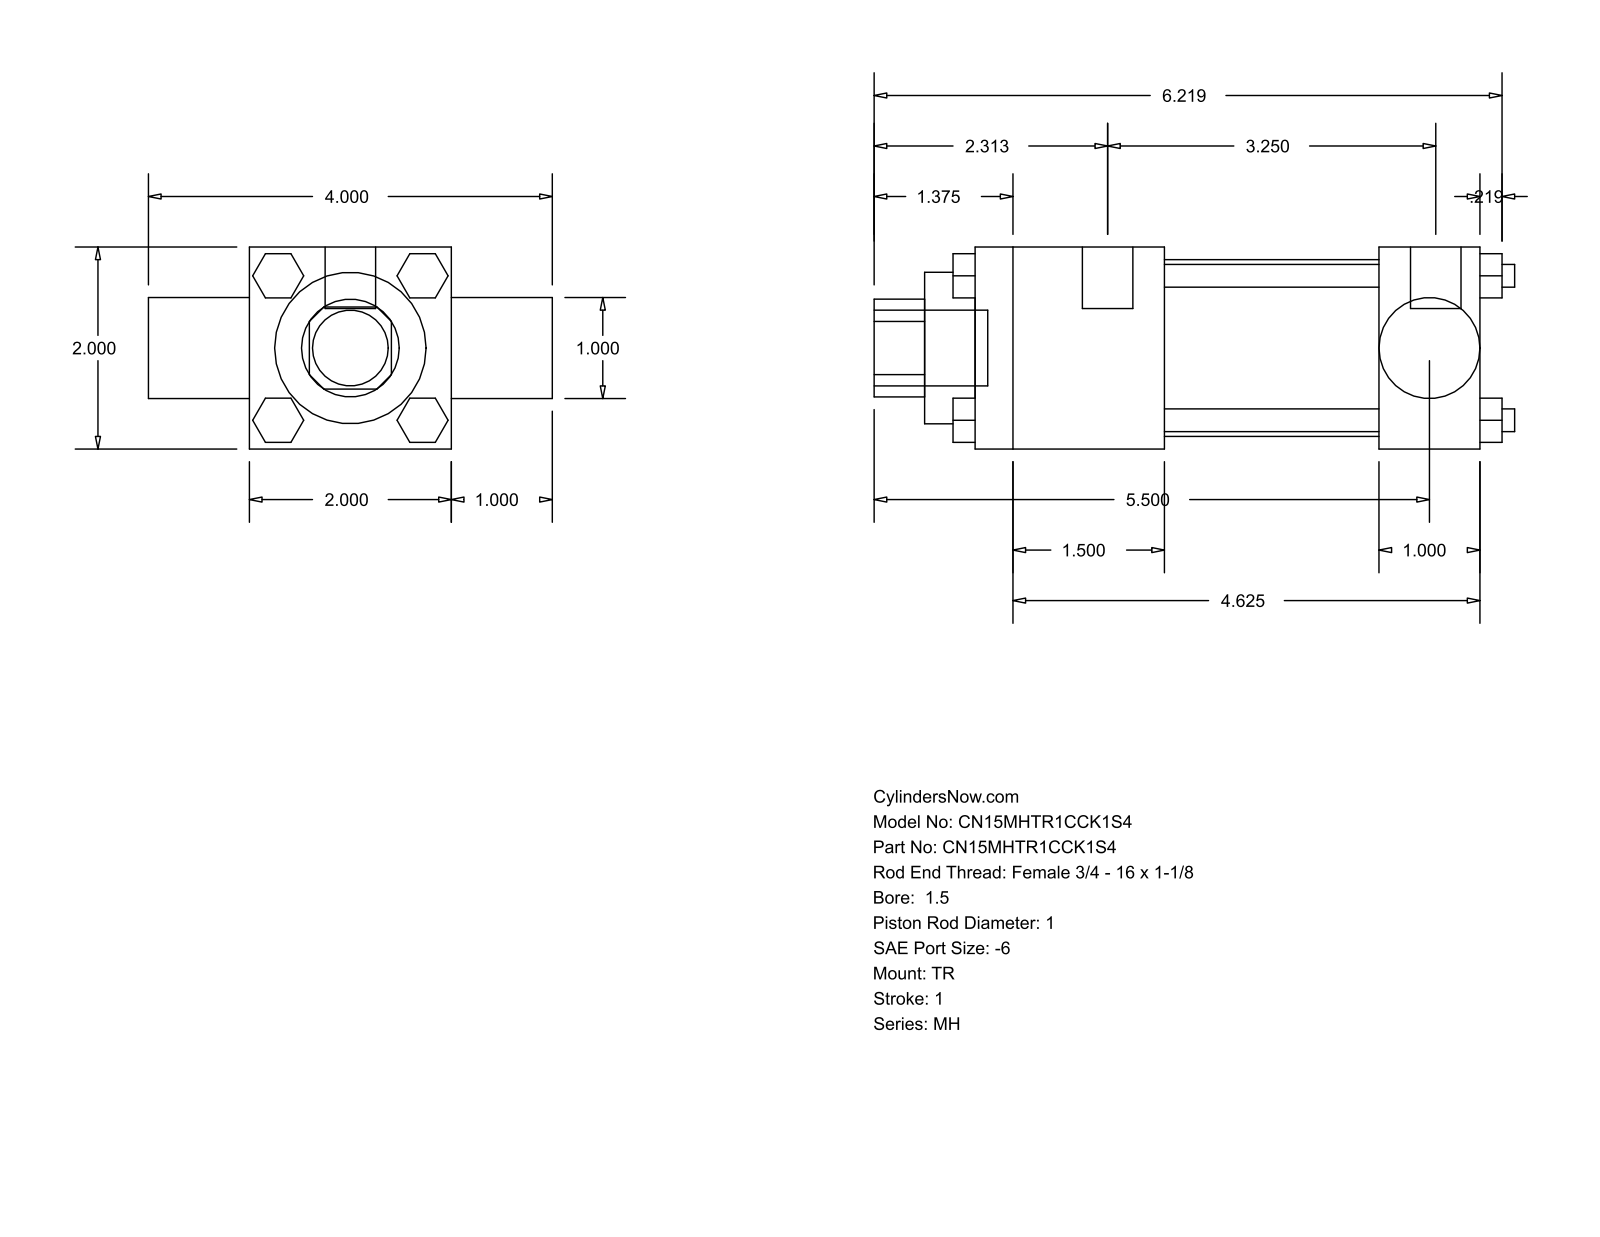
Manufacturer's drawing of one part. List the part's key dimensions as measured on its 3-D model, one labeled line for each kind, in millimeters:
Part name (STEP PRODUCT): MH_TR__0150_1
STEP written by: GSSL Pune (CONFIG_CONTROL_DESIGN)
Units: millimetres
Bodies: 0 solids, 120 faces (92 planar, 28 cylindrical, 0 other)
Overall size (bounding box): 161.13 × 101.6 × 50.8
Round holes (diameter × count): ⌀25.35 ×1, ⌀25.4 ×1, ⌀38.1 ×1, ⌀44.45 ×1
Round bosses / shafts (diameter × count): ⌀5.71 ×4, ⌀5.56 ×3, ⌀12.7 ×2, ⌀19.05 ×1
Partial cylindrical surfaces — rounded edges, fillets, slot ends (radius × count): R12.29 ×1
Main face-to-face distances: 50.8, 25.4, 101.6, 127, 76.2, 47.63, 79.37, 53.97, 132.56, 12.7
